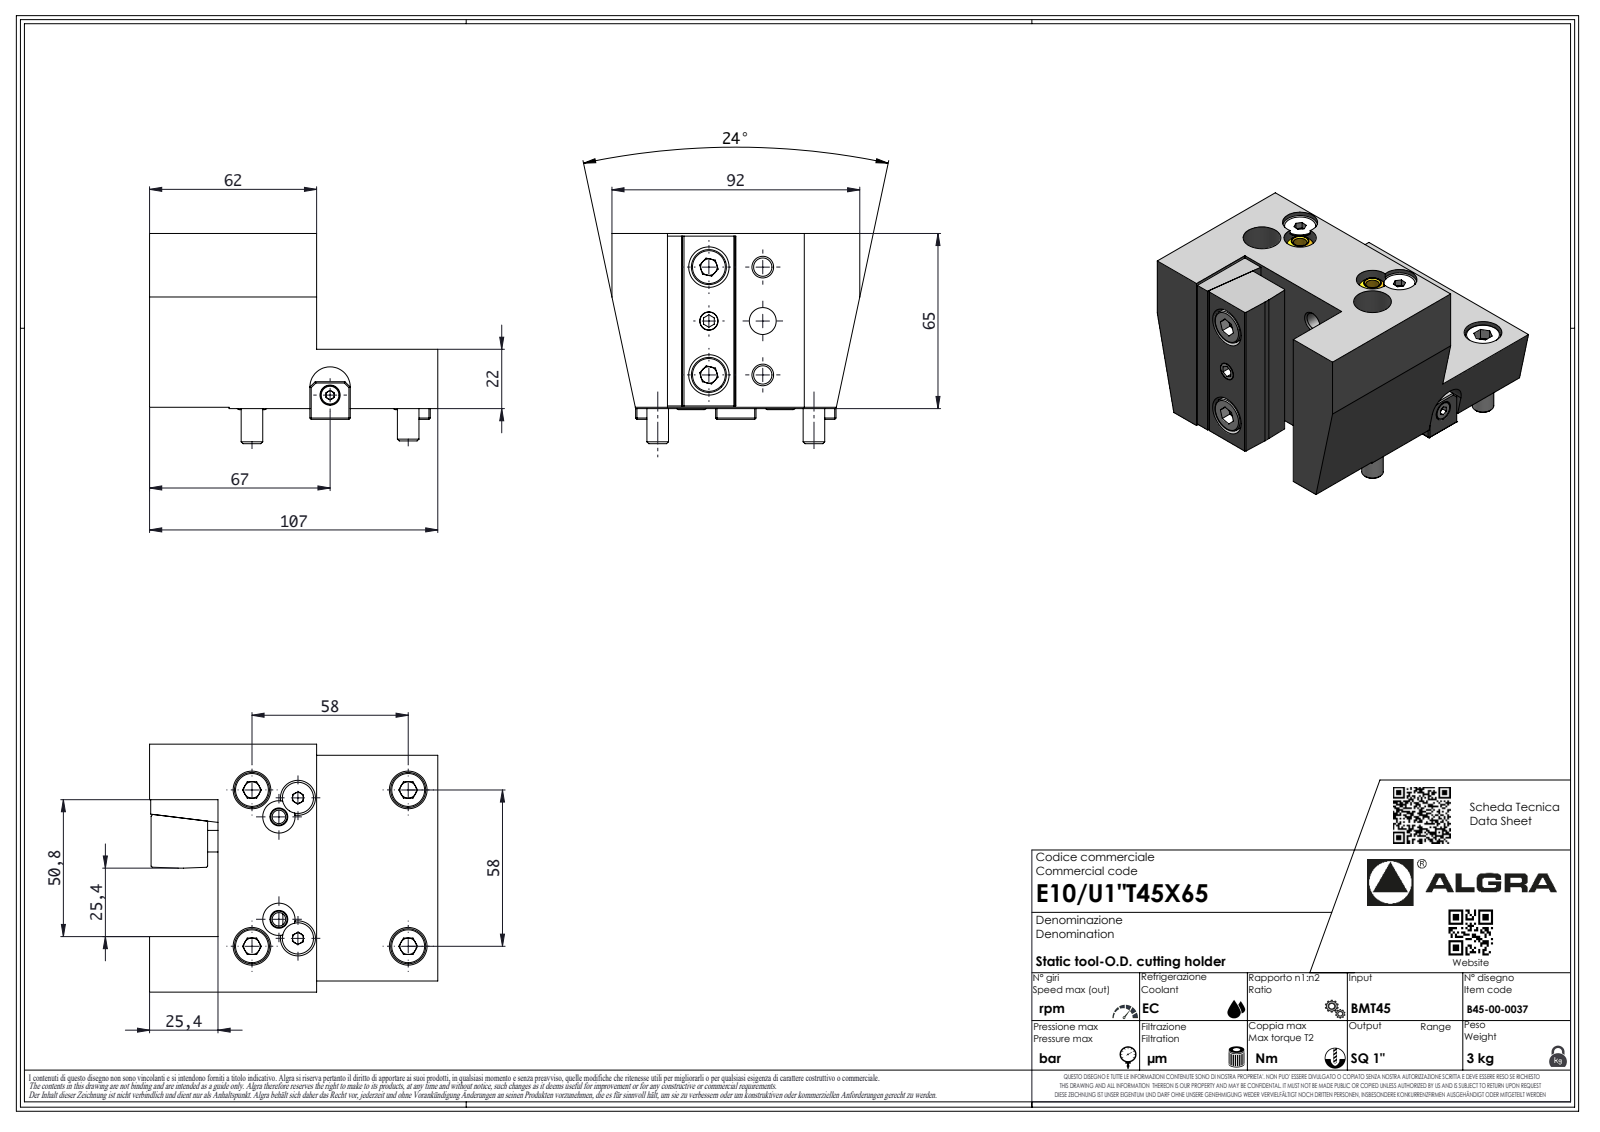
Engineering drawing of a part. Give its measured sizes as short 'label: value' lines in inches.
name: E10U1T45X65
written by: SolidWorks 2023 (AUTOMOTIVE_DESIGN)
unit: in
bodies: 1 solid, 343 faces (261 planar, 32 cylindrical, 50 other)
size: 4.213 × 3.622 × 3.071
volume: 23.52 in³; area: 66.01 in²
holes: 1× ⌀0.083
bosses: 4× ⌀0.315, 1× ⌀0.251, 1× ⌀0.067
rounds: 7× R0.013, 7× R0.02, 7× R0.146, 1× R0.008, 1× R0.551
face distances: 2.559, 0.866, 1.693, 2.441, 1, 1.441, 4.213, 3.213, 1.772, 0.016
